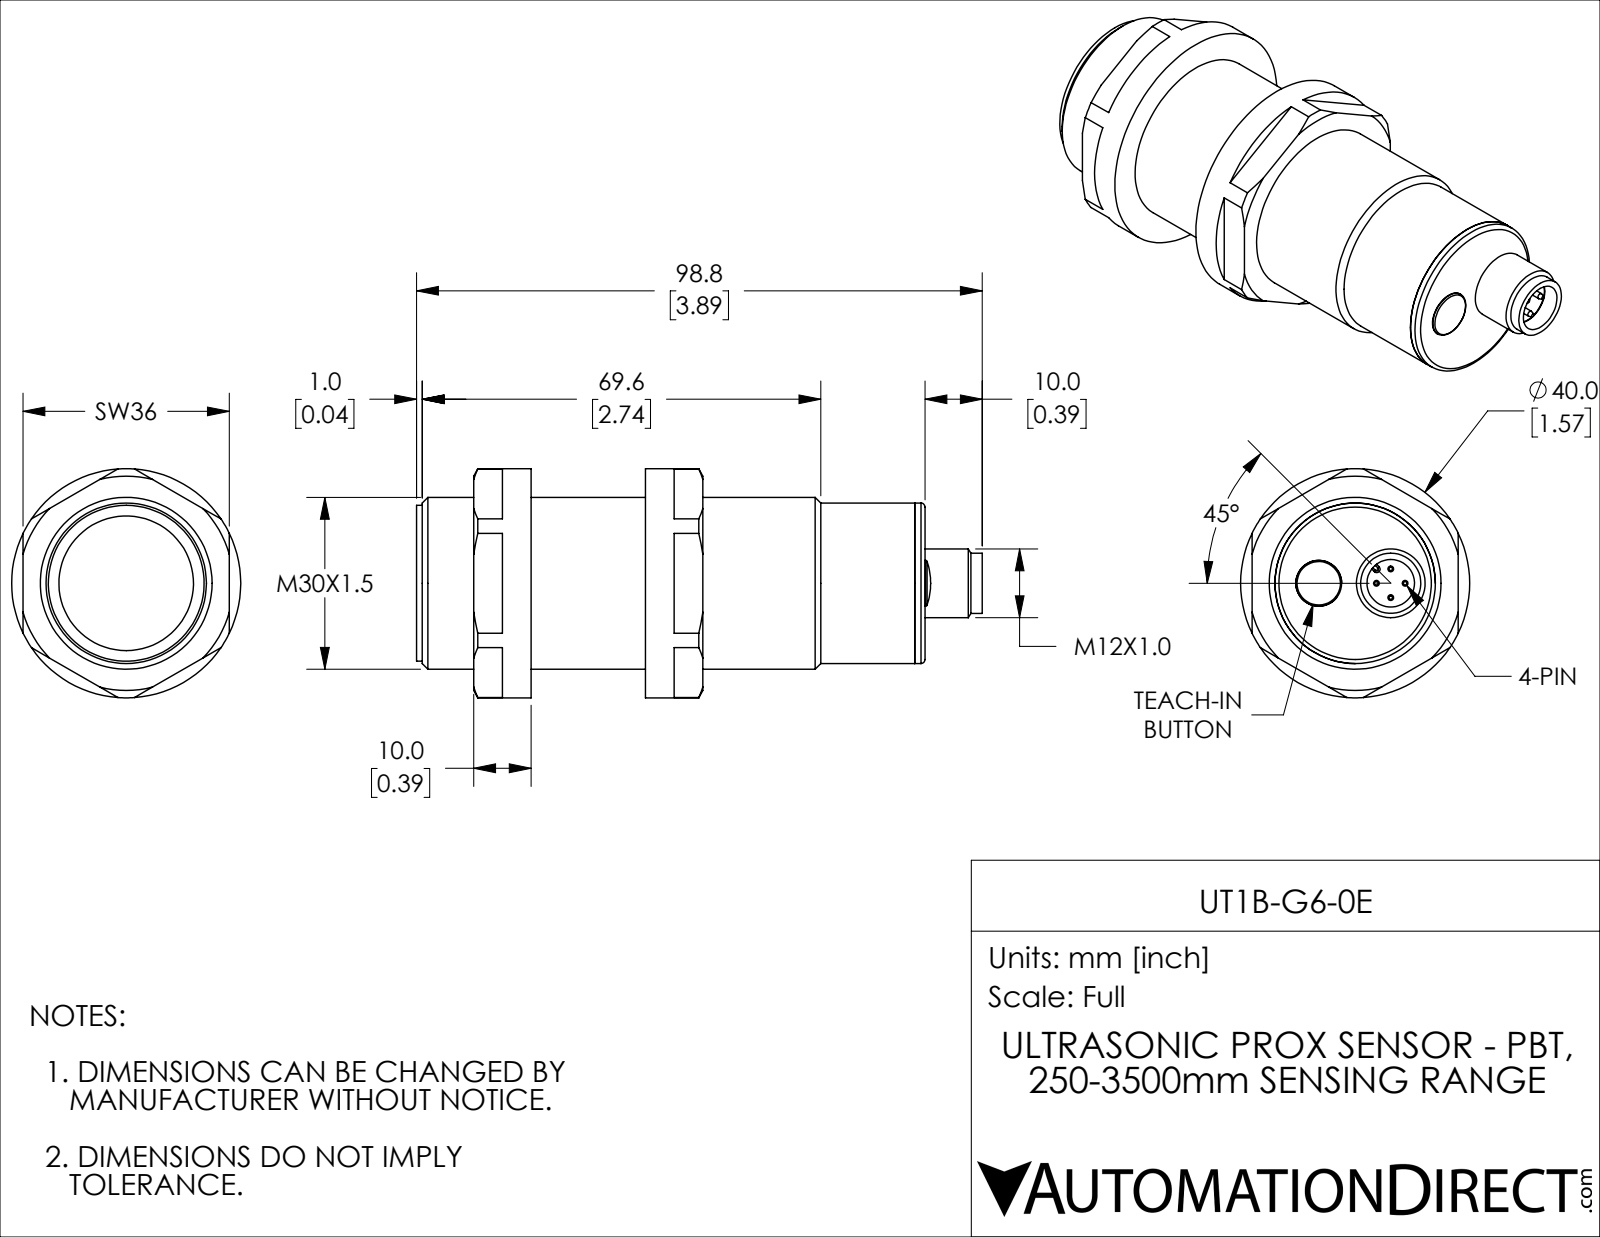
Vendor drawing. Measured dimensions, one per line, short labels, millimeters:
name: UT1B-G6-0E
written by: SolidWorks 2018 (AUTOMOTIVE_DESIGN)
unit: mm
bodies: 7 solids, 158 faces (58 planar, 53 cylindrical, 47 other)
size: 98.8 × 40 × 40
volume: 71 077 mm³; area: 19 881 mm²
holes: 4× ⌀1.8, 1× ⌀8, 1× ⌀8.3, 1× ⌀9.45, 1× ⌀23.5, 1× ⌀30
bosses: 4× ⌀1, 1× ⌀40, 1× ⌀28, 1× ⌀27.2, 1× ⌀12, 1× ⌀10.5, 1× ⌀9.25
rounds: 2× R0.3, 1× R0.6
face distances: 86, 10, 30, 20, 5, 40, 47, 39, 19, 67
hole spacings: 2.5, 3.54, 5, 6.7, 12.83, 3.72, 6.22, 6.36
